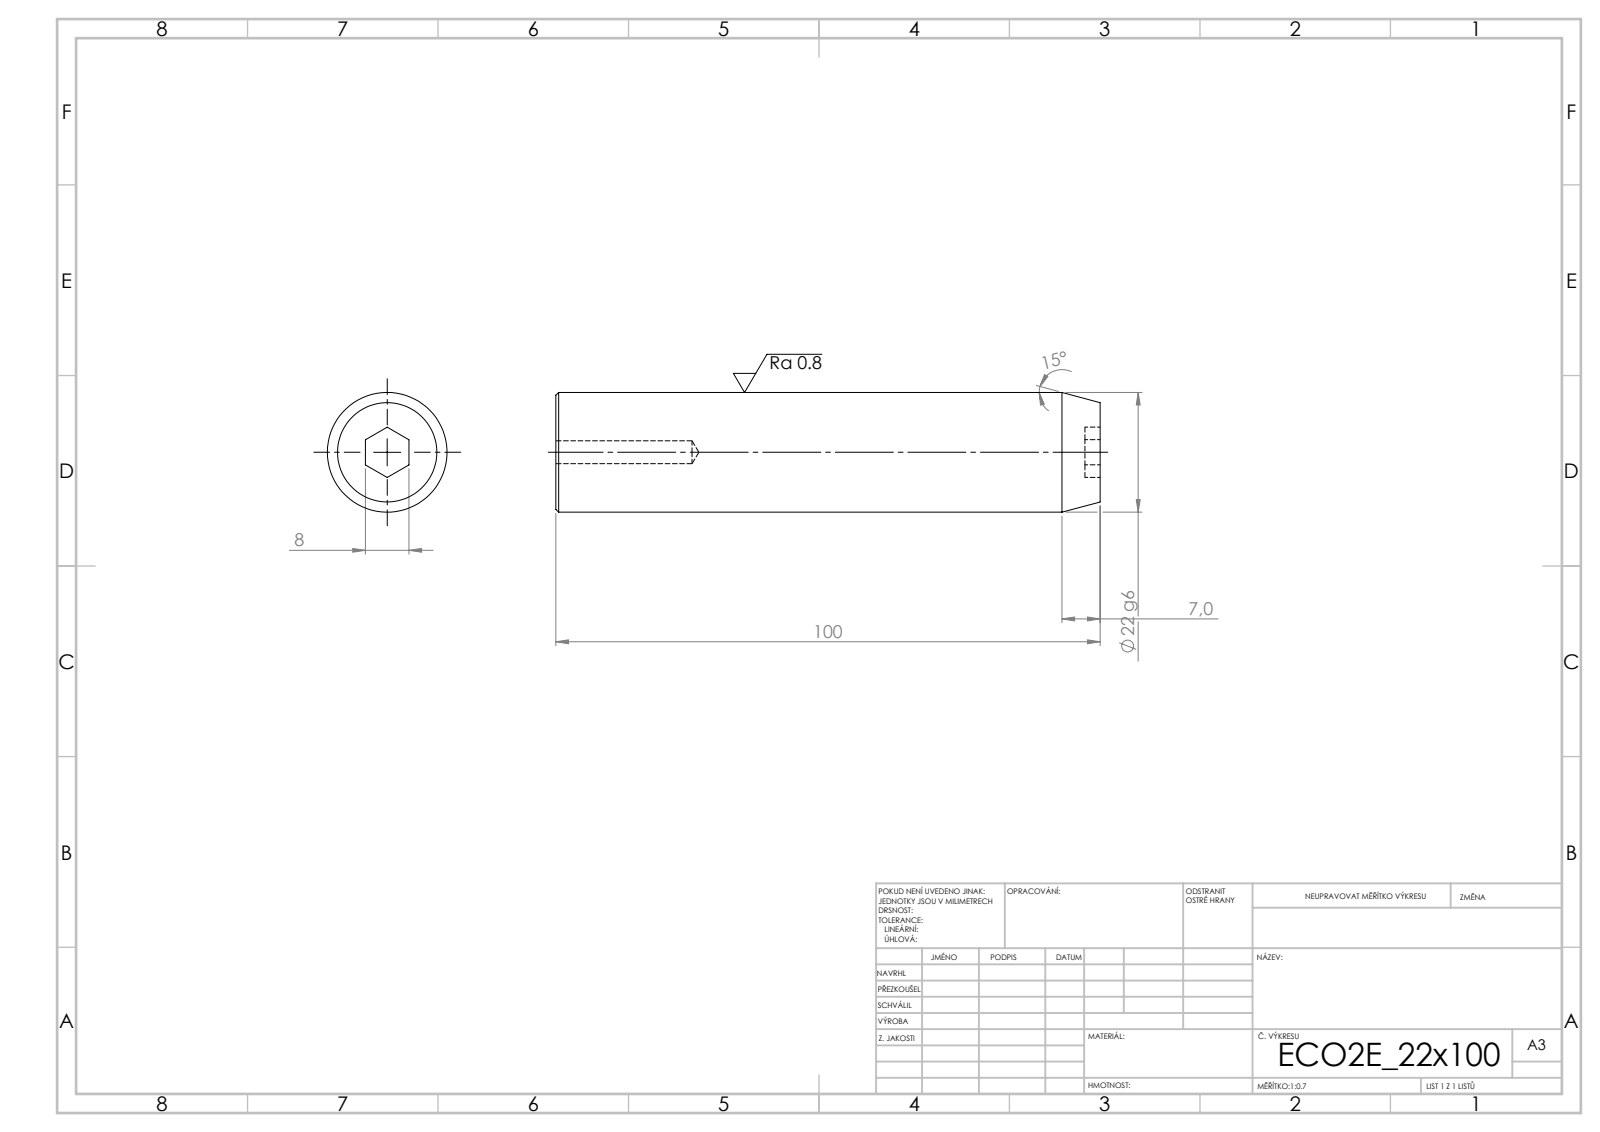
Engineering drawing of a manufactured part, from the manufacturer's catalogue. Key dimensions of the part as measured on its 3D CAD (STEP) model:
STEP written by: SolidWorks 2019 (CONFIG_CONTROL_DESIGN)
Units: millimetres
Bodies: 1 solid, 19 faces (9 planar, 4 cylindrical, 6 other)
Overall size (bounding box): 100 × 22 × 22
Volume: 37 069 mm³ · Surface area: 7 917 mm²
Round holes (diameter × count): ⌀4.2 ×1
Round bosses / shafts (diameter × count): ⌀22 ×1
Main face-to-face distances: 100, 2.8, 97.2, 8
